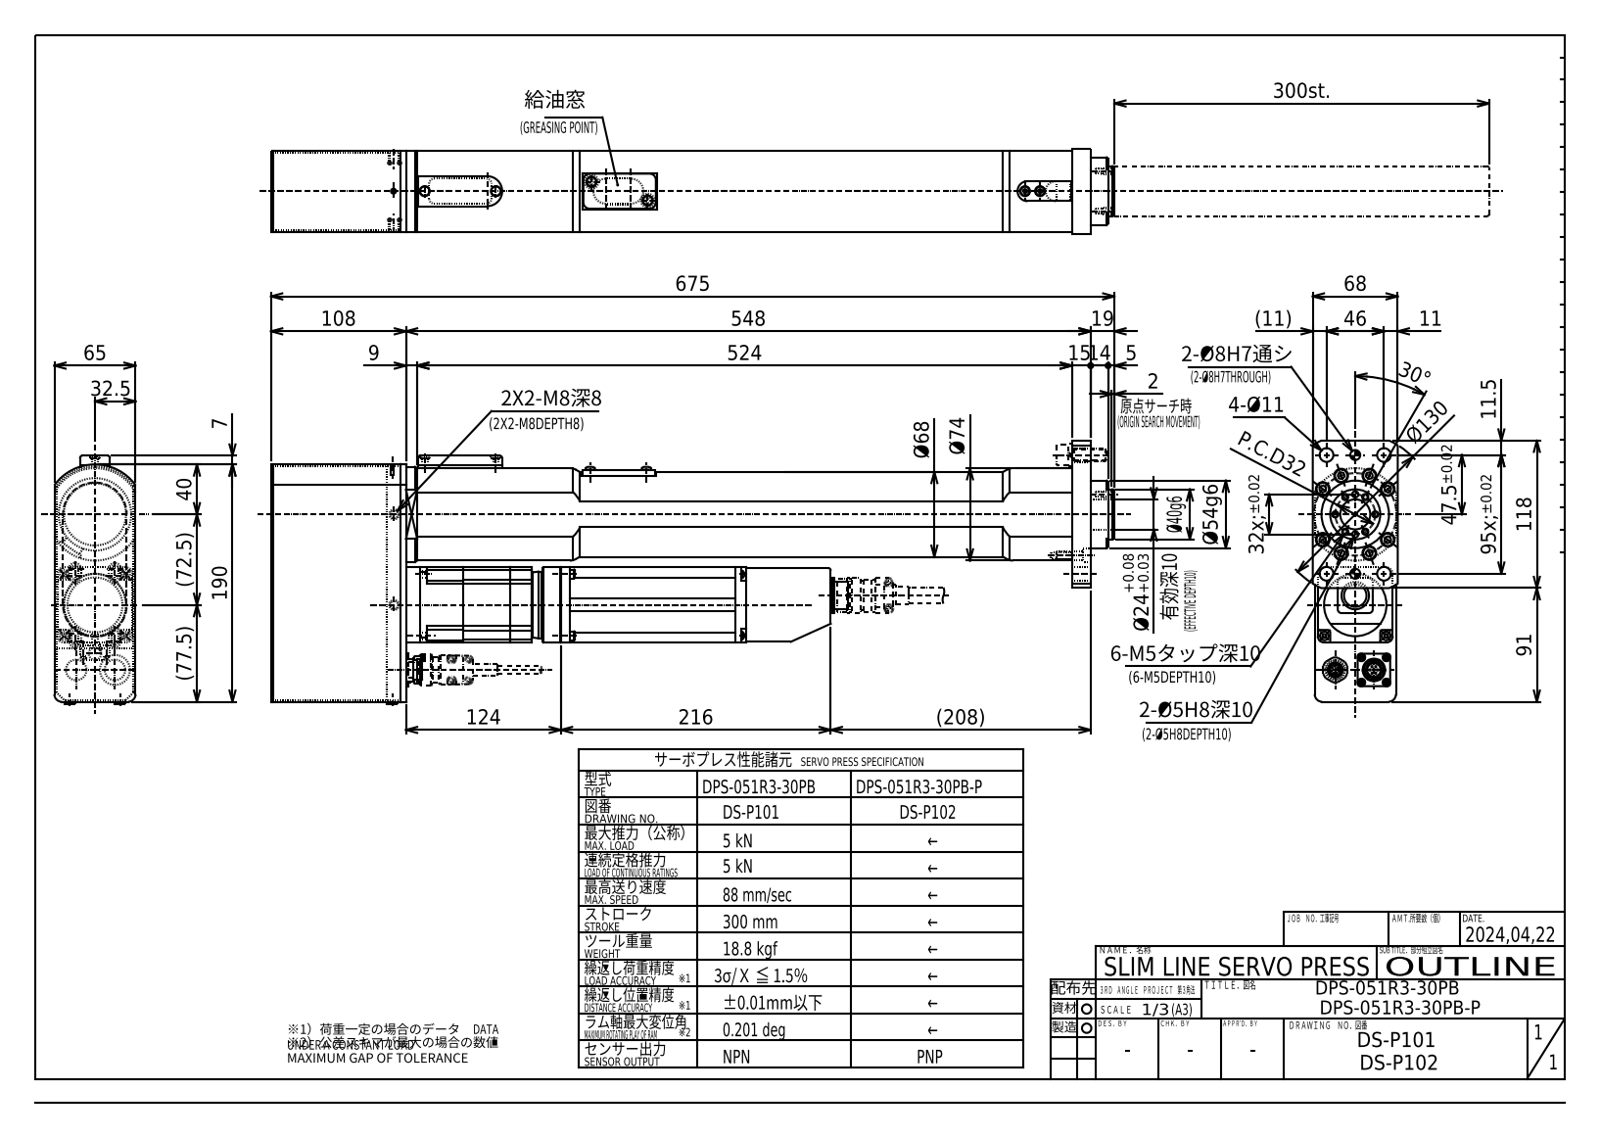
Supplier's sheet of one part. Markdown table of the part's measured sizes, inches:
| quantity | value |
| --- | --- |
| part name | DPS-051R3-30PB(-P)(DS-P101_P102)_OUTLINE; DPS-051R3-30PB_OUTLINE-HOLDER; DPS-051R3-30PB_OUTLINE-SHAFT |
| STEP written by | Autodesk Inventor 2023 (CONFIG_CONTROL_DESIGN) |
| units | inches |
| bodies | 4 solids, 1302 faces (642 planar, 316 cylindrical, 344 other) |
| overall size | 26.575 × 8.287 × 2.677 |
| volume | 272.7 in³ |
| surface area | 704.9 in² |
| round holes (diameter × count) | 0.163 × 6, 0.315 × 6, 0.126 × 4, 0.177 × 4, 0.433 × 4, 0.047 × 3, 0.128 × 3, 0.097 × 2, 0.197 × 2, 0.335 × 2, 0.157 × 1, 0.268 × 1 |
| round bosses / shafts (diameter × count) | 0.157 × 10, 0.039 × 7, 0.276 × 6, 0.335 × 4, 0.315 × 3, 0.055 × 3, 0.63 × 2, 2.677 × 1 |
| partial cylindrical surfaces (radius × count) | 0.079 × 27, 0.197 × 20, 0.008 × 16, 0.157 × 7, 0.02 × 6, 0.065 × 6, 0.089 × 6, 0.118 × 6 |
| main face-to-face distances | 2.559, 0.098, 2.362, 2.461, 0.591, 0.433, 4.232, 1.929, 1.87, 25.827 |
| hole center spacings | 0.63, 0.326, 0.557, 0.582, 0.787, 0.891, 0.906, 1.091 |
